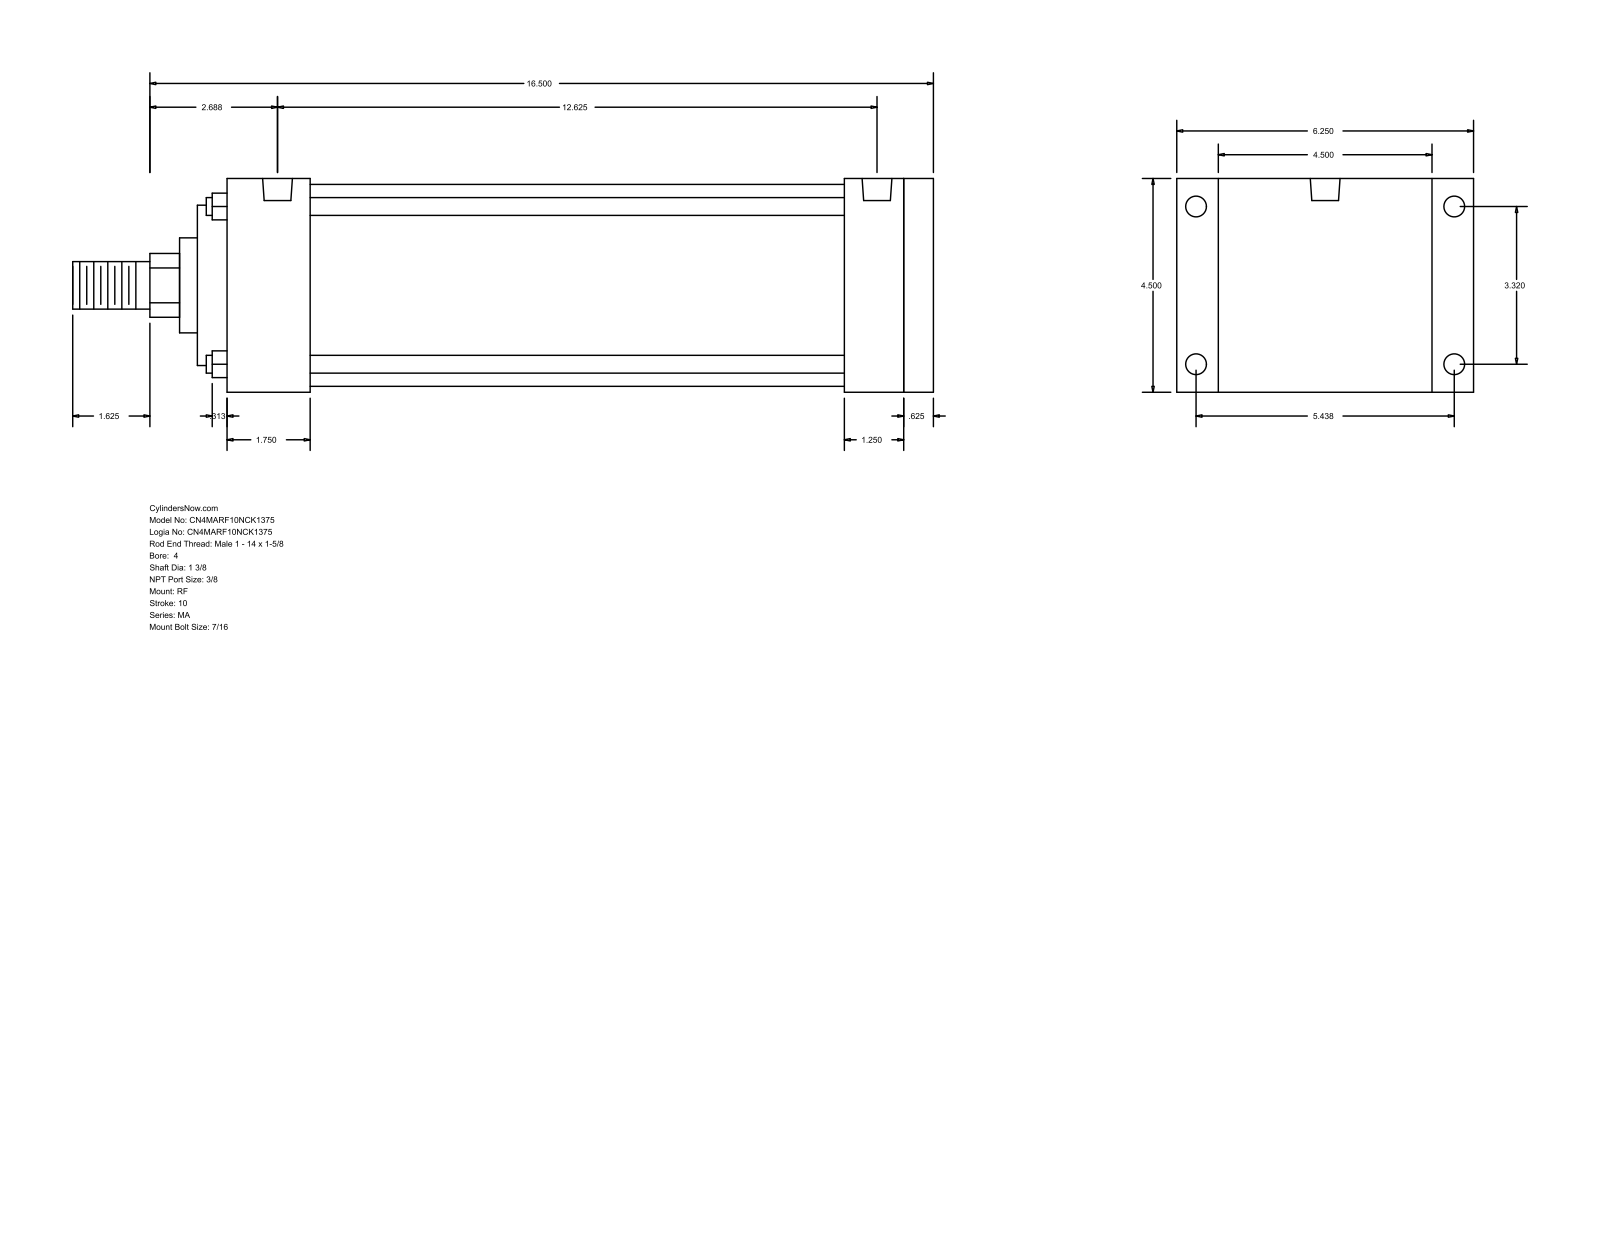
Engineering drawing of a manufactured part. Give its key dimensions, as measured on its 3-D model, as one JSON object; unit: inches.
{"part_name": "MA_RF__0400_1.375", "step_written_by": "GSSL Pune (CONFIG_CONTROL_DESIGN)", "units": "inches", "bodies": {"solids": 0, "faces": 94, "planar": 65, "cylindrical": 29, "other": 0}, "overall_size": [18.125, 6.25, 4.5], "round_holes": [[0.437, 8], [0.627, 2]], "round_bosses_or_shafts": [[0.375, 4], [4.25, 1], [3.375, 1], [2, 1], [1.375, 1], [1, 1]], "partial_cylinders_radius": [[0.672, 1]], "face_to_face_distances": [4.5, 14.875, 0.625, 14.25, 15.5, 0.875, 5.375, 13.625, 13, 1.25], "hole_center_spacings": [3.32, 5.438, 6.371, 12.25, 0.187, 0.188, 12.437, 12.438]}
